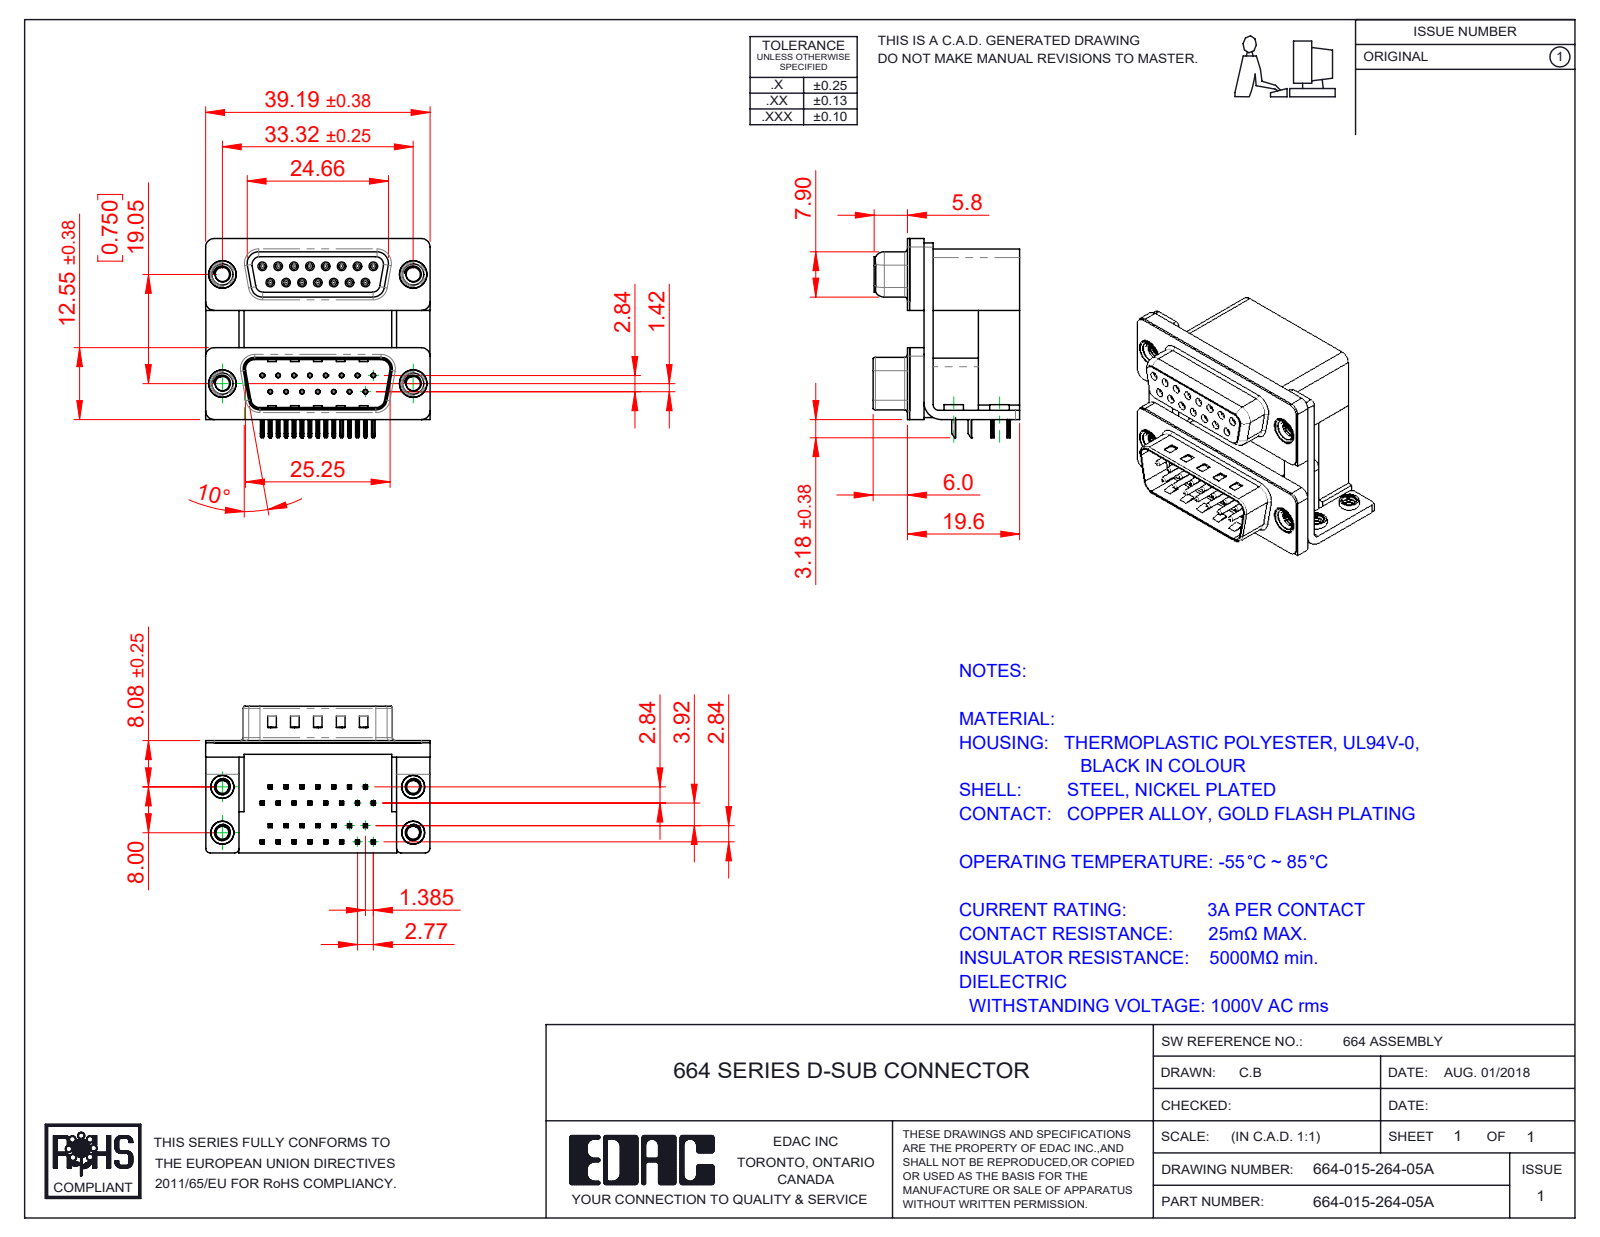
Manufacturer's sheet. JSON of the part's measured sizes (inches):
{"part_name": "664 Housing Lower_15 Contacts; 664 Threaded Rivet_M3; 664 Contact Top Lower; 664 Mounting Bracket_ThruM (+8 more)", "step_written_by": "SolidWorks 2020 (CONFIG_CONTROL_DESIGN)", "units": "inches", "bodies": {"solids": 45, "faces": 4056, "planar": 2027, "cylindrical": 1098, "other": 931}, "overall_size": [1.543, 1.369, 1.008], "volume_in3": 0.927, "surface_area_in2": 26.52, "round_holes": [[0.031, 30], [0.014, 15], [0.035, 15], [0.089, 4], [0.098, 4], [0.108, 4], [0.126, 4], [0.138, 4], [0.157, 4], [0.189, 4], [0.197, 4]], "round_bosses_or_shafts": [[0.047, 15], [0.03, 15], [0.193, 4], [0.187, 4], [0.157, 4], [0.154, 4], [0.134, 4]], "partial_cylinders_radius": [[0.004, 120], [0.006, 60], [0.01, 60], [0.005, 30], [0.014, 30], [0.059, 16], [0.013, 15], [0.02, 12]], "face_to_face_distances": [0.016, 0.756, 0.657, 0.098, 0.283, 0.472, 0.374, 0.421, 0.086, 0.114], "hole_center_spacings": [0.124, 0.109, 0.758, 0.218, 0.781, 0.327, 0.75, 0.818]}
